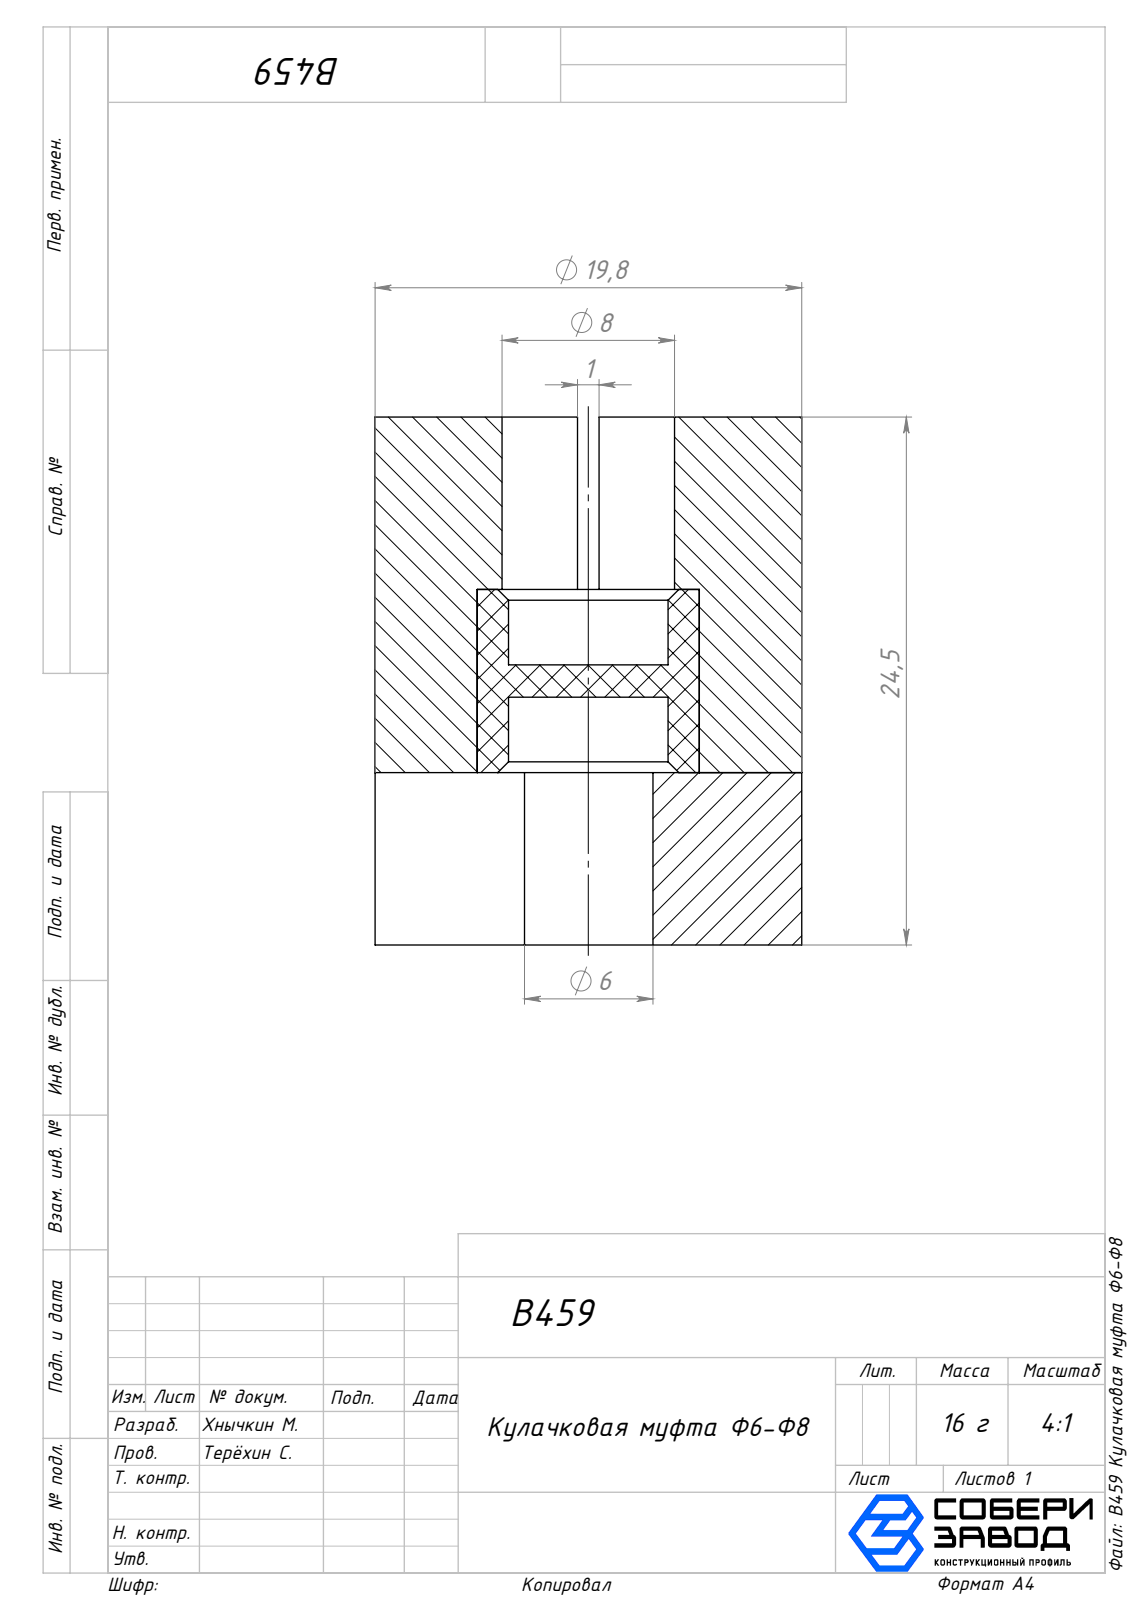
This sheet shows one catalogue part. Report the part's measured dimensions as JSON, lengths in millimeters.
{"part_name": "Верх_00; Середина_00; Низ_00; B459 Кулачковая муфта Ф6-Ф8", "step_written_by": "SolidWorks 2025 (AUTOMOTIVE_DESIGN)", "units": "millimeters", "bodies": {"solids": 3, "faces": 56, "planar": 24, "cylindrical": 28, "other": 4}, "overall_size": [24.5, 19.8, 19.8], "volume_mm3": 6506, "surface_area_mm2": 4526, "round_holes": [[6, 1], [7.4, 1], [8, 1]], "round_bosses_or_shafts": [[19.8, 1]], "partial_cylinders_radius": [[6, 8]], "face_to_face_distances": [8, 16.5, 8.5, 24.5, 4.65, 5.65, 1, 11.5, 13, 3.5]}
